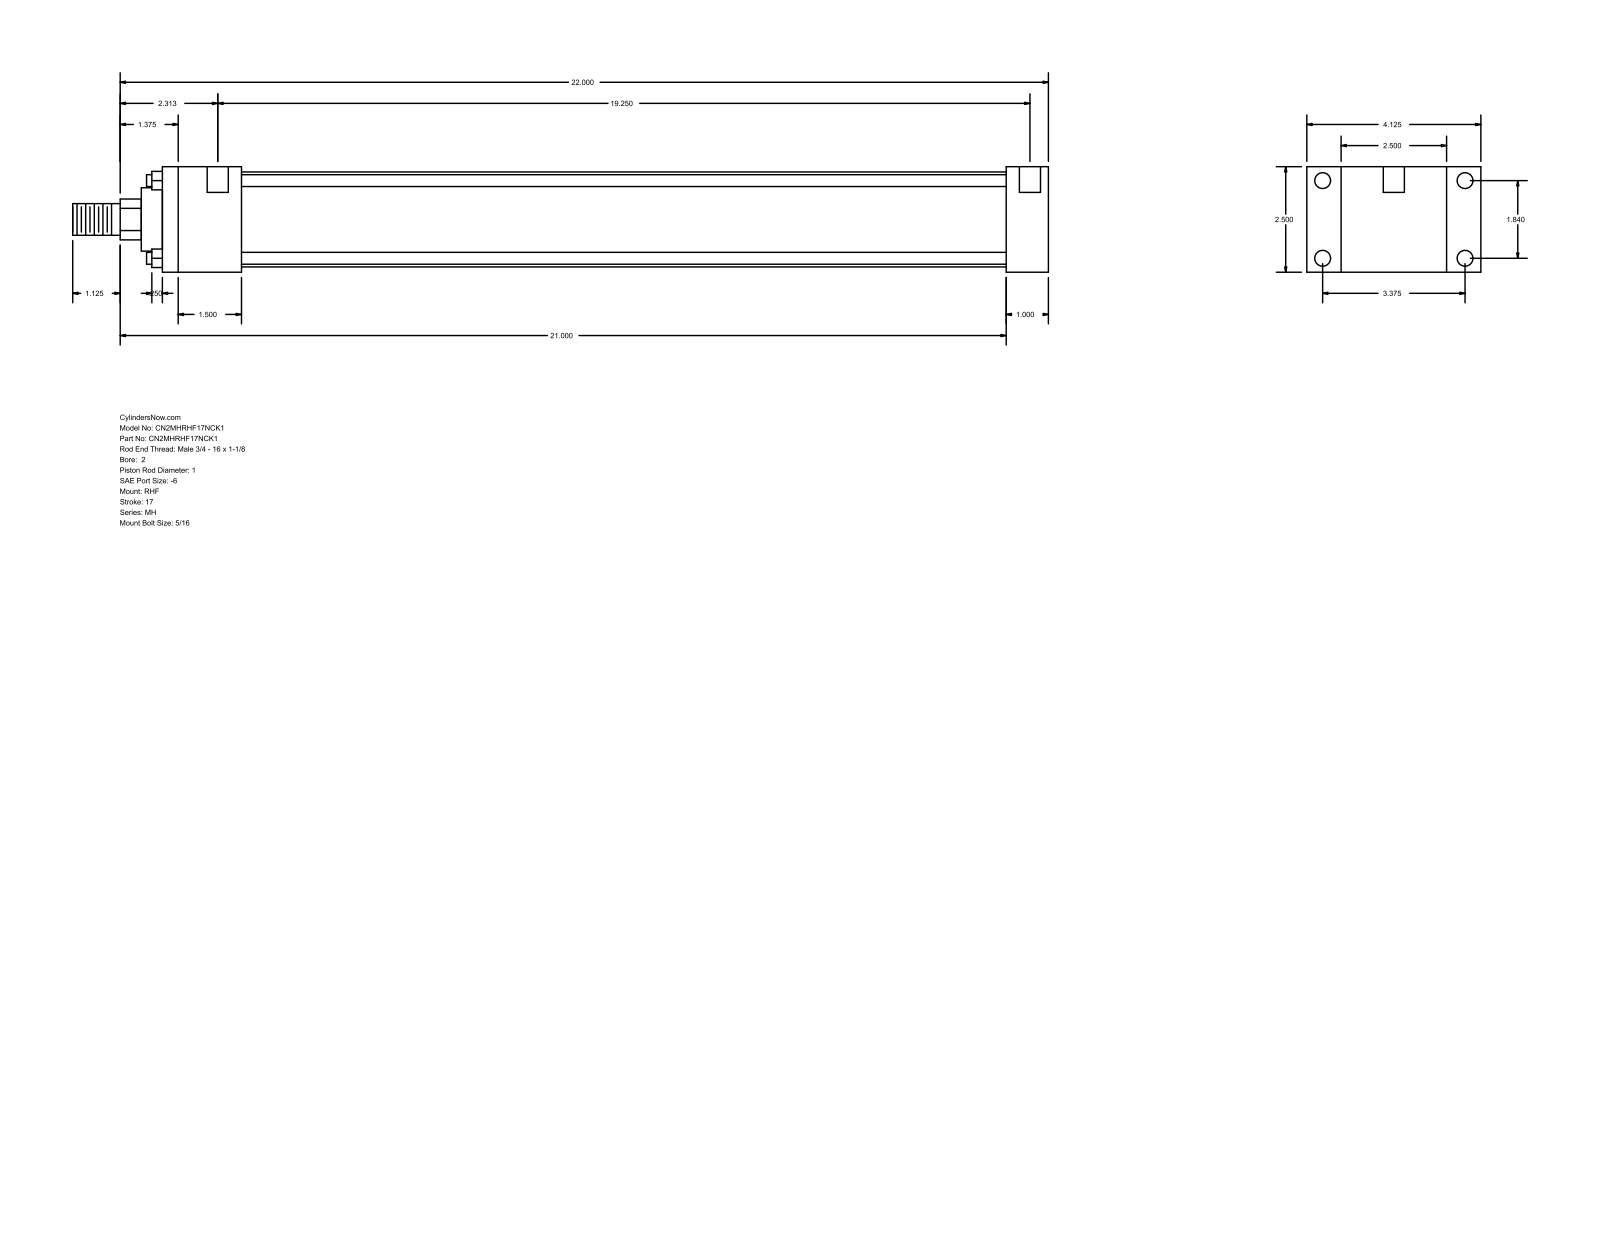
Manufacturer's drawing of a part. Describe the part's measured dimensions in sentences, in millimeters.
The part is named "MH_RHF__0200_1". Its 3-D file was written by "GSSL Pune (CONFIG_CONTROL_DESIGN)". It is 0 solids with 88 faces: 60 planar, 28 cylindrical and 0 other. Overall it measures 587.38 by 104.78 by 63.5 millimeters. Round holes: 4 of diameter 5.56, 4 of diameter 9.53, 2 of diameter 12.7. Round bosses or shafts: 4 of diameter 7.14, 1 of diameter 57.15, 1 of diameter 38.1, 1 of diameter 25.4, 1 of diameter 19.05. Partial cylindrical surfaces (rounded edges, fillets, slot ends): 1 of radius 12.29. The main face-to-face distances are 63.5, 25.4, 20.64, 84.14, 533.4, 508, 104.78, 47.63, 460.37, 485.77. The hole center spacings are 46.74, 85.72, 97.63, 496.88, 3.17, 4.76, 488.95, 492.12.
